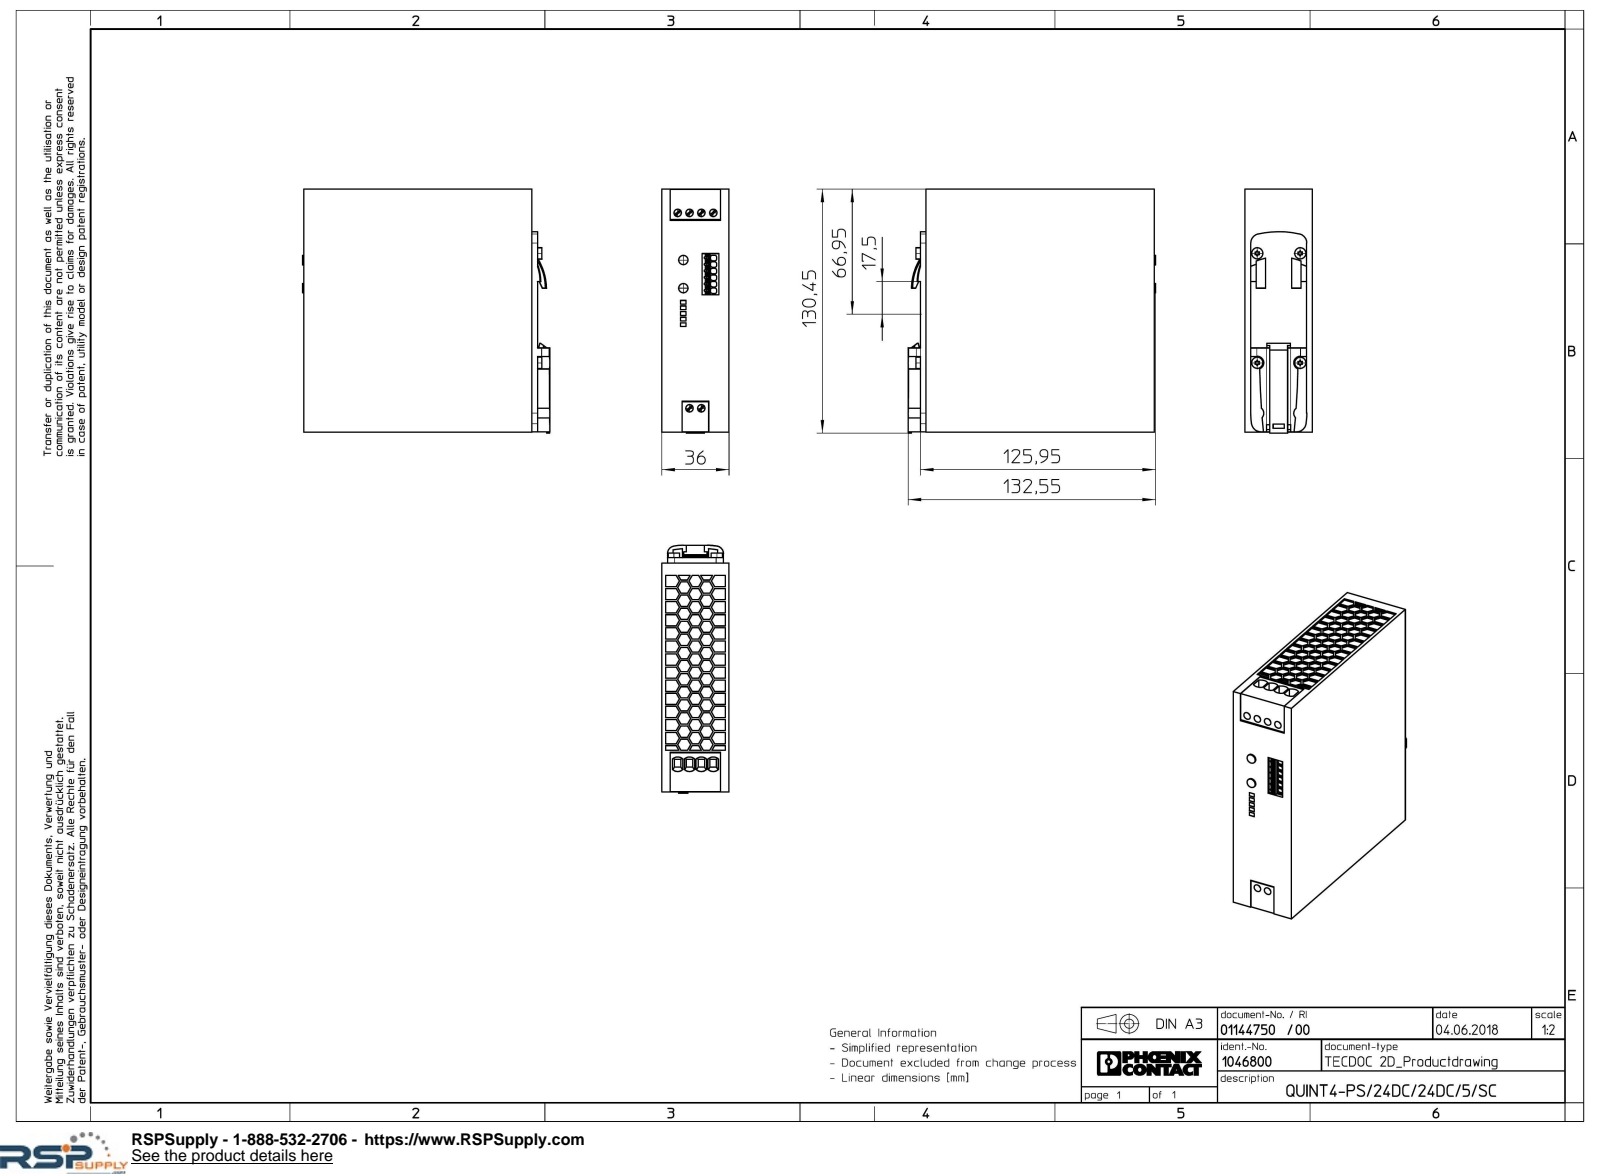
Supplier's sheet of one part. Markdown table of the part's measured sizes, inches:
| quantity | value |
| --- | --- |
| part name | QUINT4_PS_24DC_24DC_5_SC-select |
| STEP written by | Creo Elements/Direct Modeling 20.1A 29-Sep-2018 (C) Parametric Technology GmbH (AUTOMOTIVE_DESIGN) |
| units | inches |
| bodies | 1 solid, 1499 faces (1338 planar, 133 cylindrical, 28 other) |
| overall size | 5.219 × 5.136 × 1.417 |
| volume | 35.47 in³ |
| surface area | 88.27 in² |
| round holes (diameter × count) | 0.157 × 6 |
| round bosses / shafts (diameter × count) | 0.236 × 4, 0.197 × 2 |
| partial cylindrical surfaces (radius × count) | 0.004 × 48, 0.038 × 12, 0.157 × 10, 0.022 × 6, 0.024 × 6, 0.365 × 6, 0.138 × 4, 0.197 × 4 |
| main face-to-face distances | 1.417, 0.031, 5.087, 5.055, 0.118, 4.931, 5.118, 4.813, 5.114, 0.028 |
| hole center spacings | 0.25, 4.122, 0.5, 4.114, 4.144, 0.75 |
